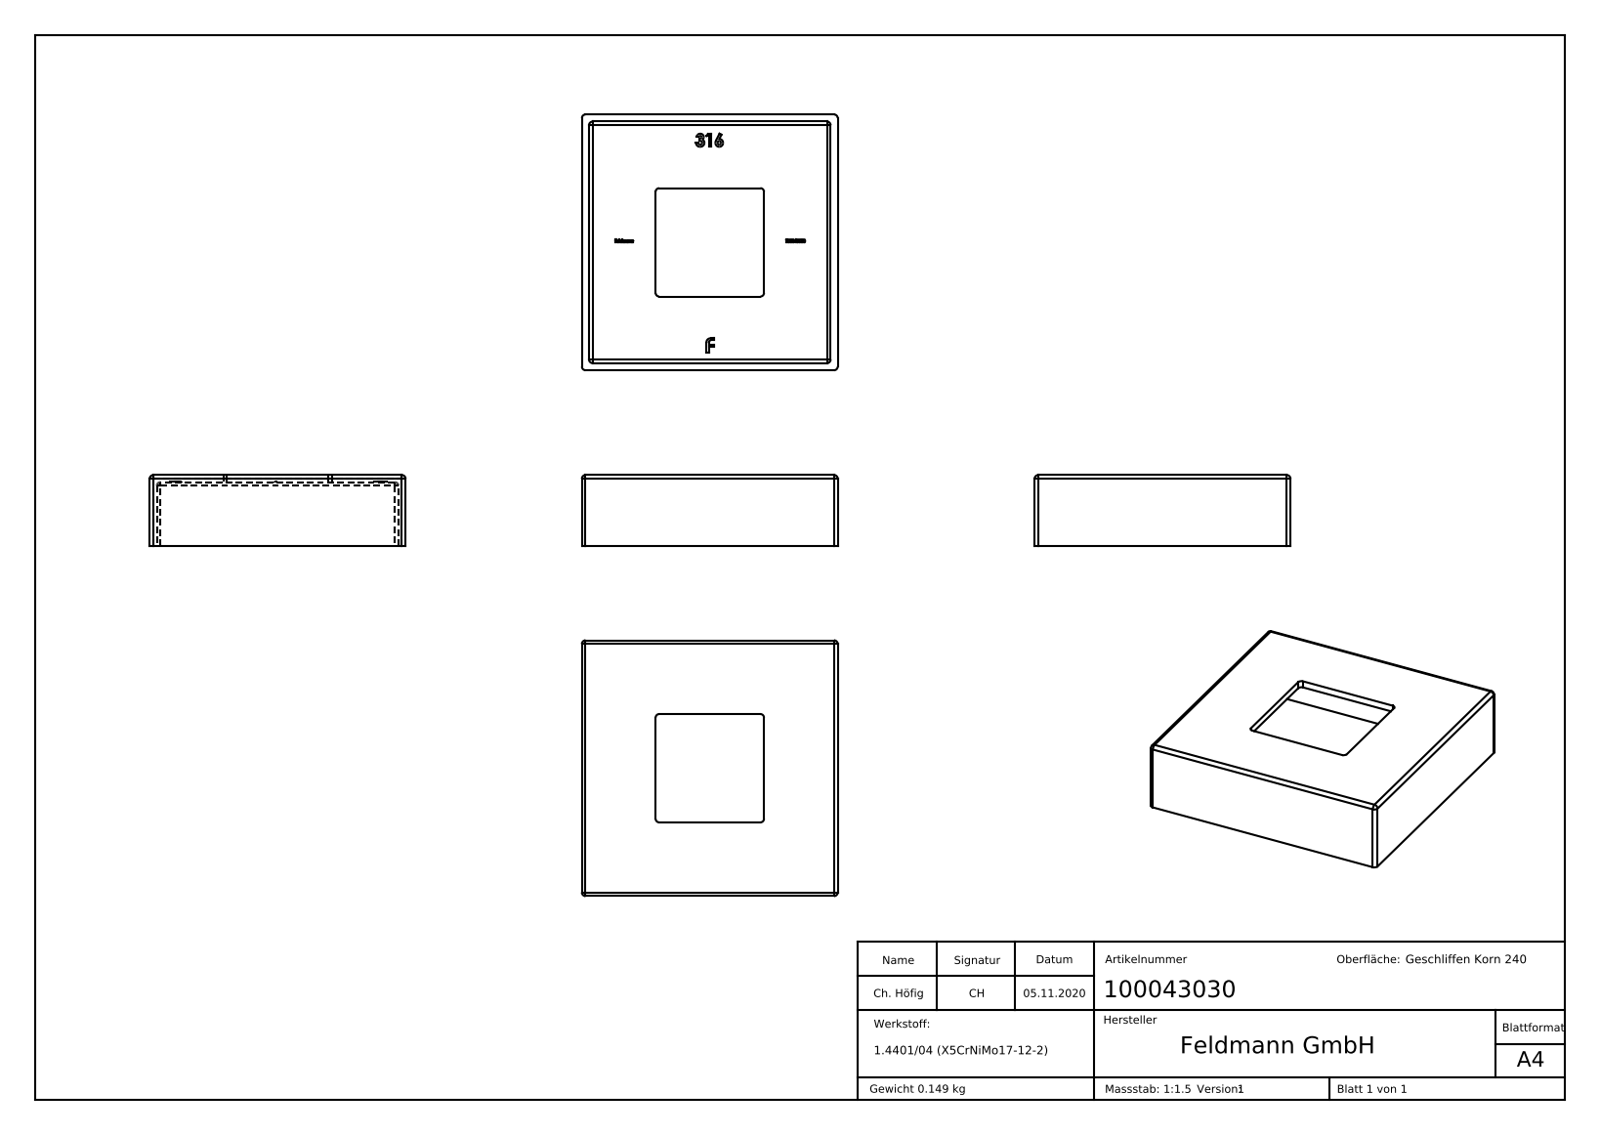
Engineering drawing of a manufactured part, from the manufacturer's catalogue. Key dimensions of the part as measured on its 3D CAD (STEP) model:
Part name (STEP PRODUCT): 100043030
STEP written by: SolidWorks 2018 (CONFIG_CONTROL_DESIGN)
Units: millimetres
Bodies: 1 solid, 319 faces (147 planar, 20 cylindrical, 152 other)
Overall size (bounding box): 72 × 72 × 20
Volume: 18 582 mm³ · Surface area: 19 110 mm²
Partial cylindrical surfaces — rounded edges, fillets, slot ends (radius × count): R1 ×20
Main face-to-face distances: 2, 70, 72, 68, 18, 20, 51.25, 49.25, 20.75, 18.75
